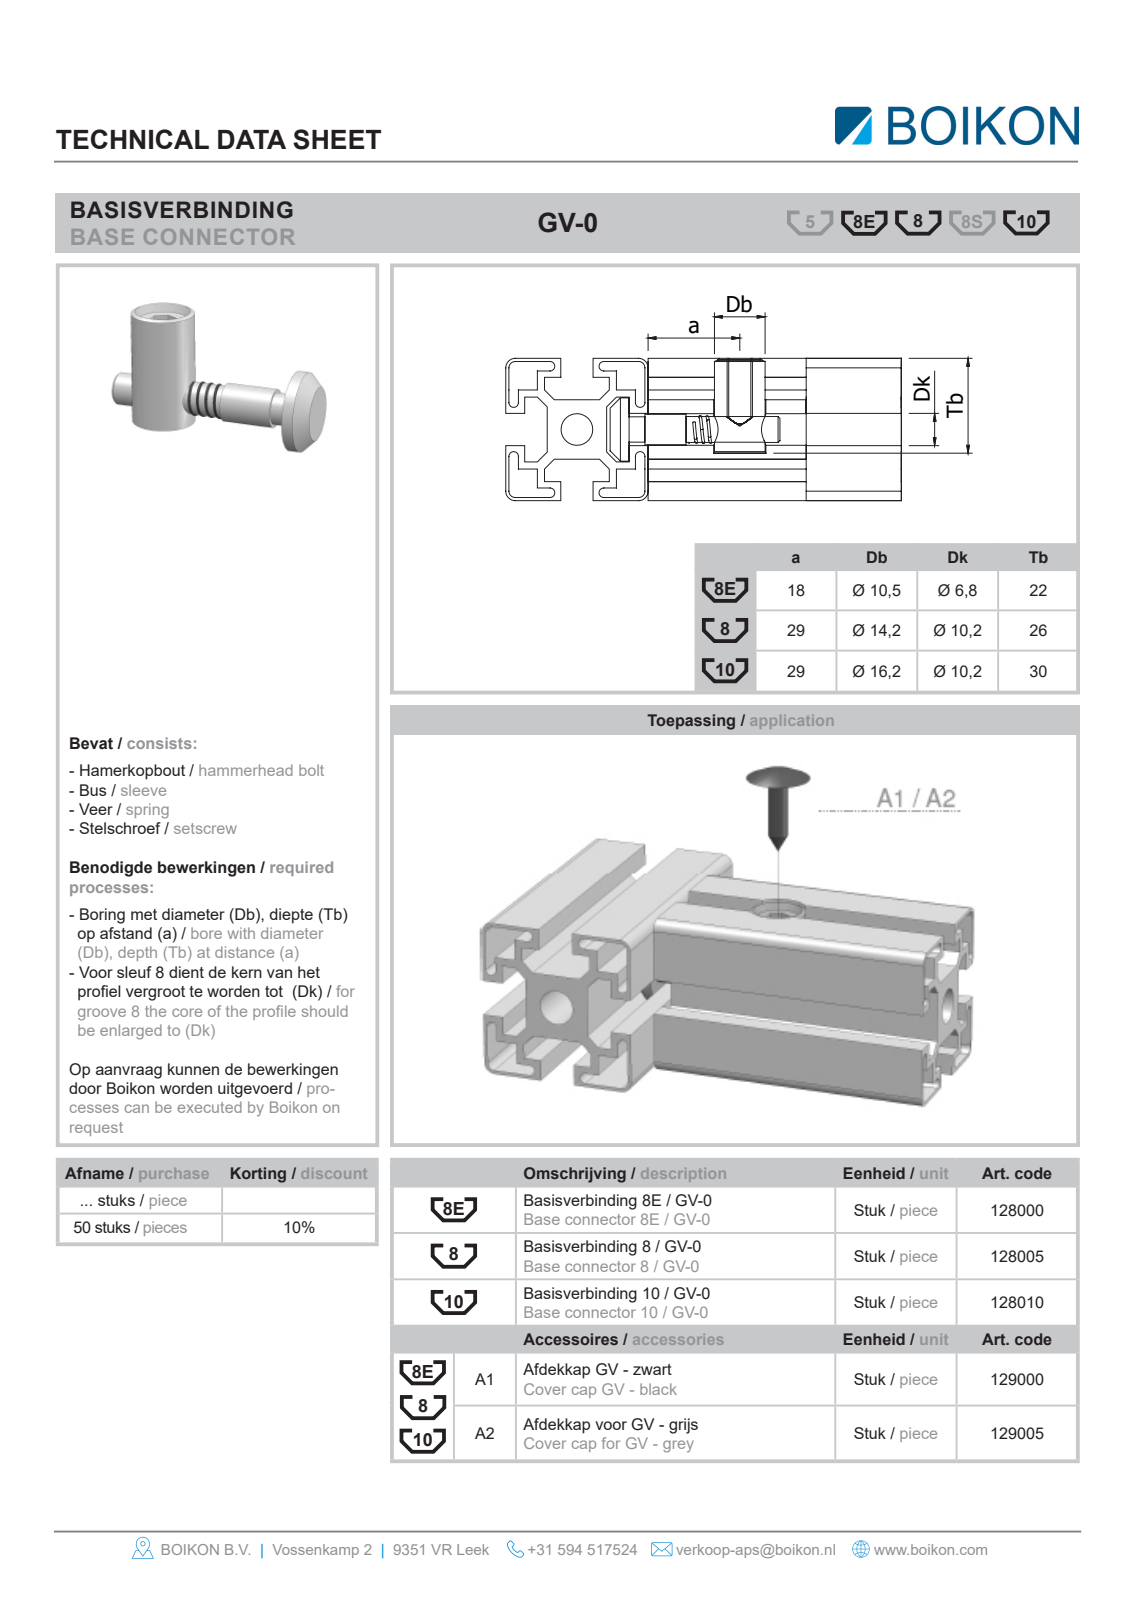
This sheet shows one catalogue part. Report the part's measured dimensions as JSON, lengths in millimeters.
{"part_name": "Root; 128005Basisverbinding 8 / GV-0BOIKON", "step_written_by": "HiCAD 2013 1802.4 Build 509 (AUTOMOTIVE_DESIGN)", "units": "millimeters", "bodies": {"solids": 1, "faces": 23, "planar": 14, "cylindrical": 6, "other": 3}, "overall_size": [51.7, 26.65, 17], "volume_mm3": 6286, "surface_area_mm2": 2994, "round_bosses_or_shafts": [[17, 1], [14, 1], [9.8, 1], [8.3, 1]], "face_to_face_distances": [5, 24, 37.2, 16, 42.2, 32.2, 9.5, 14.5, 46.7, 51.7]}
